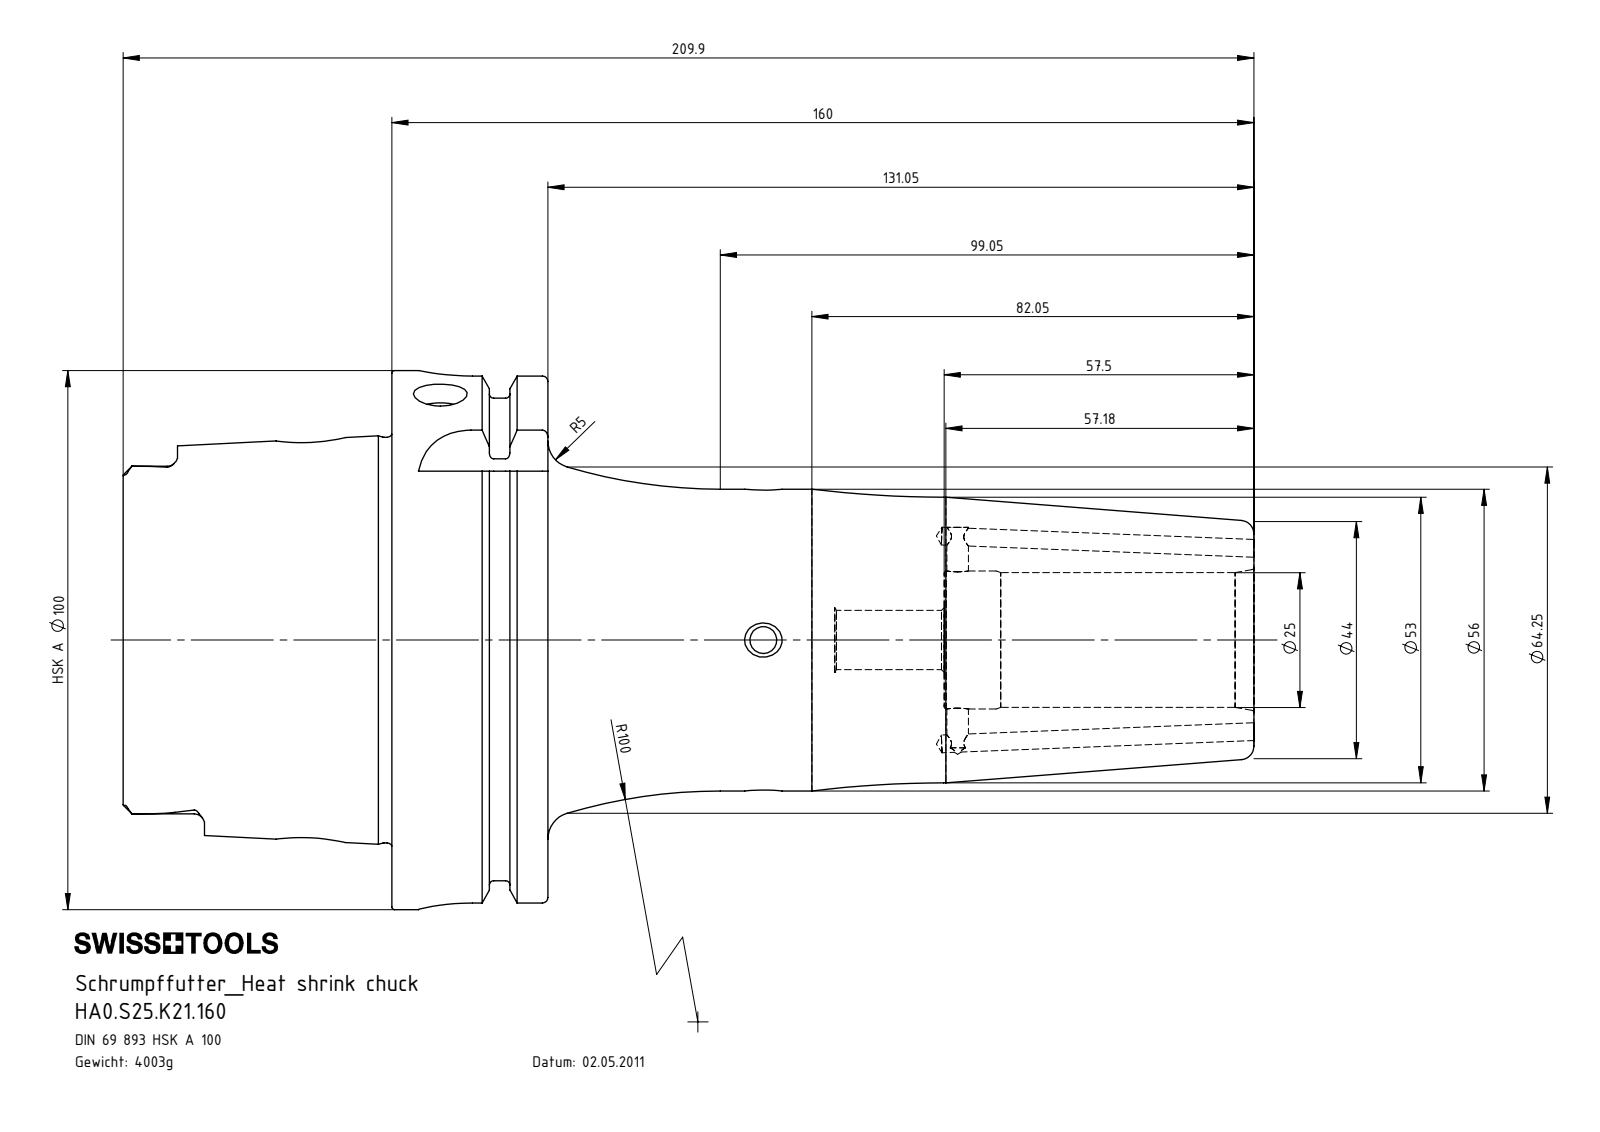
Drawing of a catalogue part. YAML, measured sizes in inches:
part_name: "HA0-S25.K21.160_C_Fertigbearbeitung; HA0.S25.K21.160; ERU-AN5.K01.020_A; ERU-CJ3.001.008"
step_written_by: "SolidWorks 2017 (CONFIG_CONTROL_DESIGN)"
units: inches
bodies: {solids: 4, faces: 305, planar: 95, cylindrical: 88, other: 122}
overall_size: [8.268, 3.937, 3.937]
volume: 31.12
surface_area: 124.6
round_holes:
  - {diameter: 0.394, count: 3}
  - {diameter: 0.13, count: 2}
  - {diameter: 0.197, count: 2}
  - {diameter: 0.472, count: 2}
  - {diameter: 0.157, count: 1}
  - {diameter: 0.236, count: 1}
  - {diameter: 0.433, count: 1}
  - {diameter: 0.886, count: 1}
  - {diameter: 0.984, count: 1}
  - {diameter: 1.008, count: 1}
  - {diameter: 1.024, count: 1}
  - {diameter: 2.087, count: 1}
round_bosses_or_shafts:
  - {diameter: 0.157, count: 2}
  - {diameter: 3.937, count: 1}
  - {diameter: 3.62, count: 1}
  - {diameter: 2.963, count: 1}
  - {diameter: 2.205, count: 1}
partial_cylinders:
  - {radius: 0.075, count: 6}
  - {radius: 0.192, count: 4}
  - {radius: 0.394, count: 4}
face_to_face_distances: [1.14, 0.49, 0.65, 1.965, 2.455, 3.104, 8.264, 6.299, 5.809, 5.159]
hole_center_spacings: [1.419, 2.439, 3.305, 4.724]
